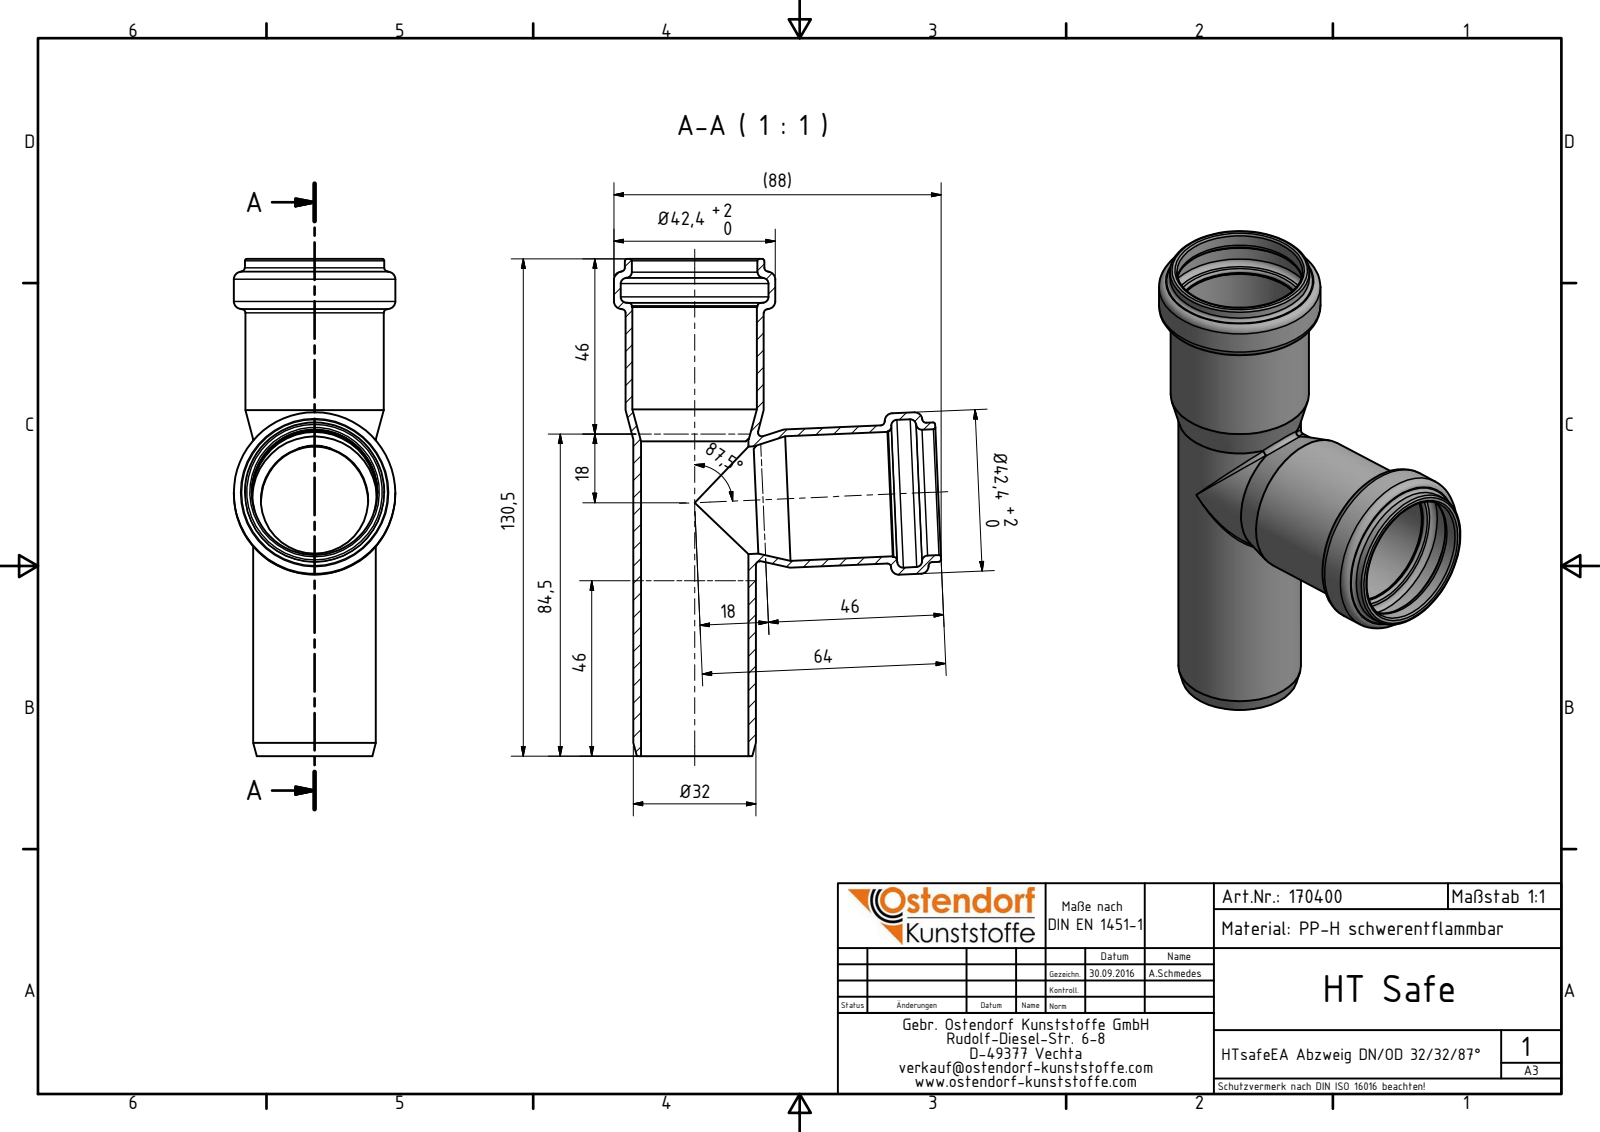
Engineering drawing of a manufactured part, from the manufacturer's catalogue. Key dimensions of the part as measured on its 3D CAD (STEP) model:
Part name (STEP PRODUCT): 170400 HTsafeEA DN_OD 32_32_87°
STEP written by: Autodesk Inventor 2016 (AUTOMOTIVE_DESIGN)
Units: millimetres
Bodies: 1 solid, 62 faces (5 planar, 20 cylindrical, 37 other)
Overall size (bounding box): 130.5 × 85.92 × 42.4
Volume: 36 129 mm³ · Surface area: 38 344 mm²
Round holes (diameter × count): ⌀33 ×3, ⌀28.2 ×2, ⌀32.7 ×2, ⌀38.8 ×2
Round bosses / shafts (diameter × count): ⌀42.4 ×2, ⌀36.6 ×2, ⌀36.3 ×2, ⌀32.2 ×2
Main face-to-face distances: 130.5, 12.62, 117.87, 12.63
